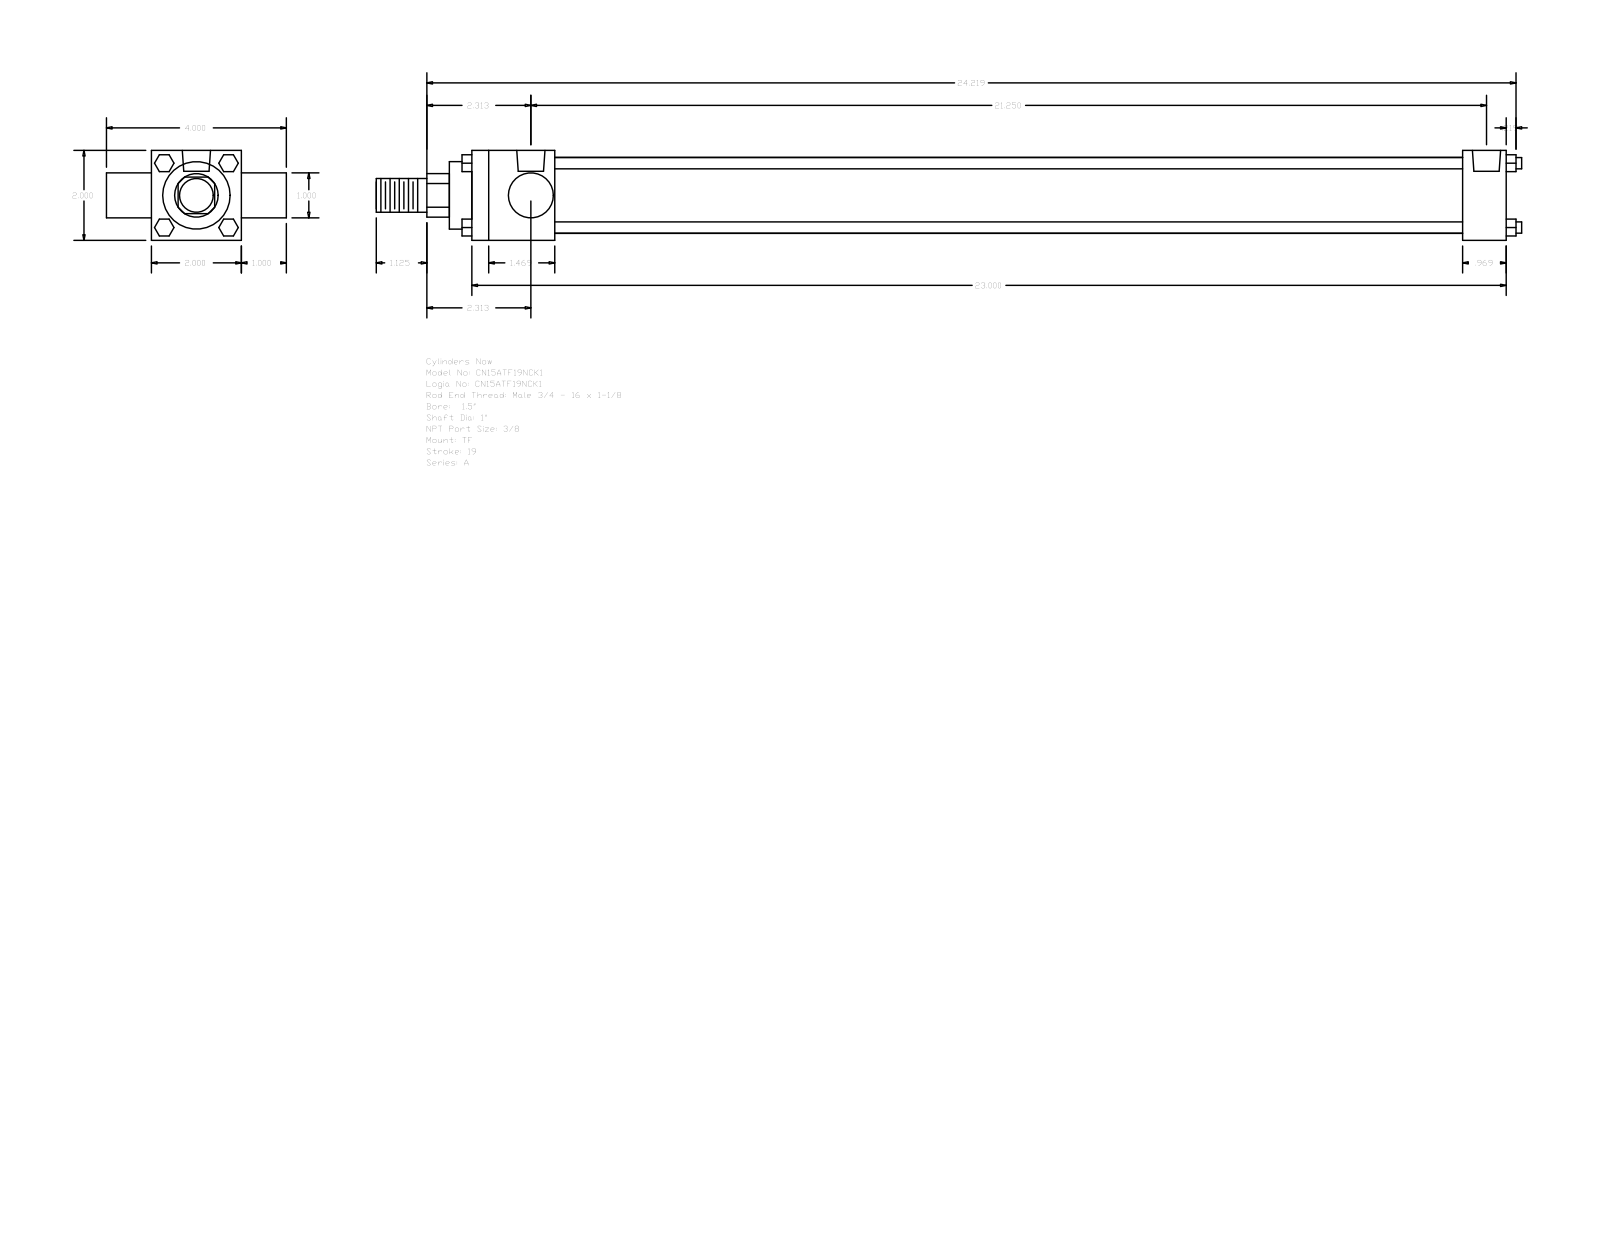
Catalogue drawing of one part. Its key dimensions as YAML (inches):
part_name: "A_TF__0150_1"
step_written_by: "GSSL Pune (CONFIG_CONTROL_DESIGN)"
units: inches
bodies: {solids: 0, faces: 120, planar: 92, cylindrical: 28, other: 0}
overall_size: [25.469, 4, 2]
round_holes:
  - {diameter: 0.219, count: 3}
  - {diameter: 0.627, count: 2}
round_bosses_or_shafts:
  - {diameter: 0.25, count: 4}
  - {diameter: 1, count: 2}
  - {diameter: 1.69, count: 1}
  - {diameter: 1.5, count: 1}
  - {diameter: 0.75, count: 1}
partial_cylinders:
  - {radius: 0.484, count: 1}
face_to_face_distances: [2, 1, 23, 3, 1.844, 22.031, 20.187, 21.156, 0.969, 0.5]
hole_center_spacings: [0.156, 21.094, 20.937, 21.25]
